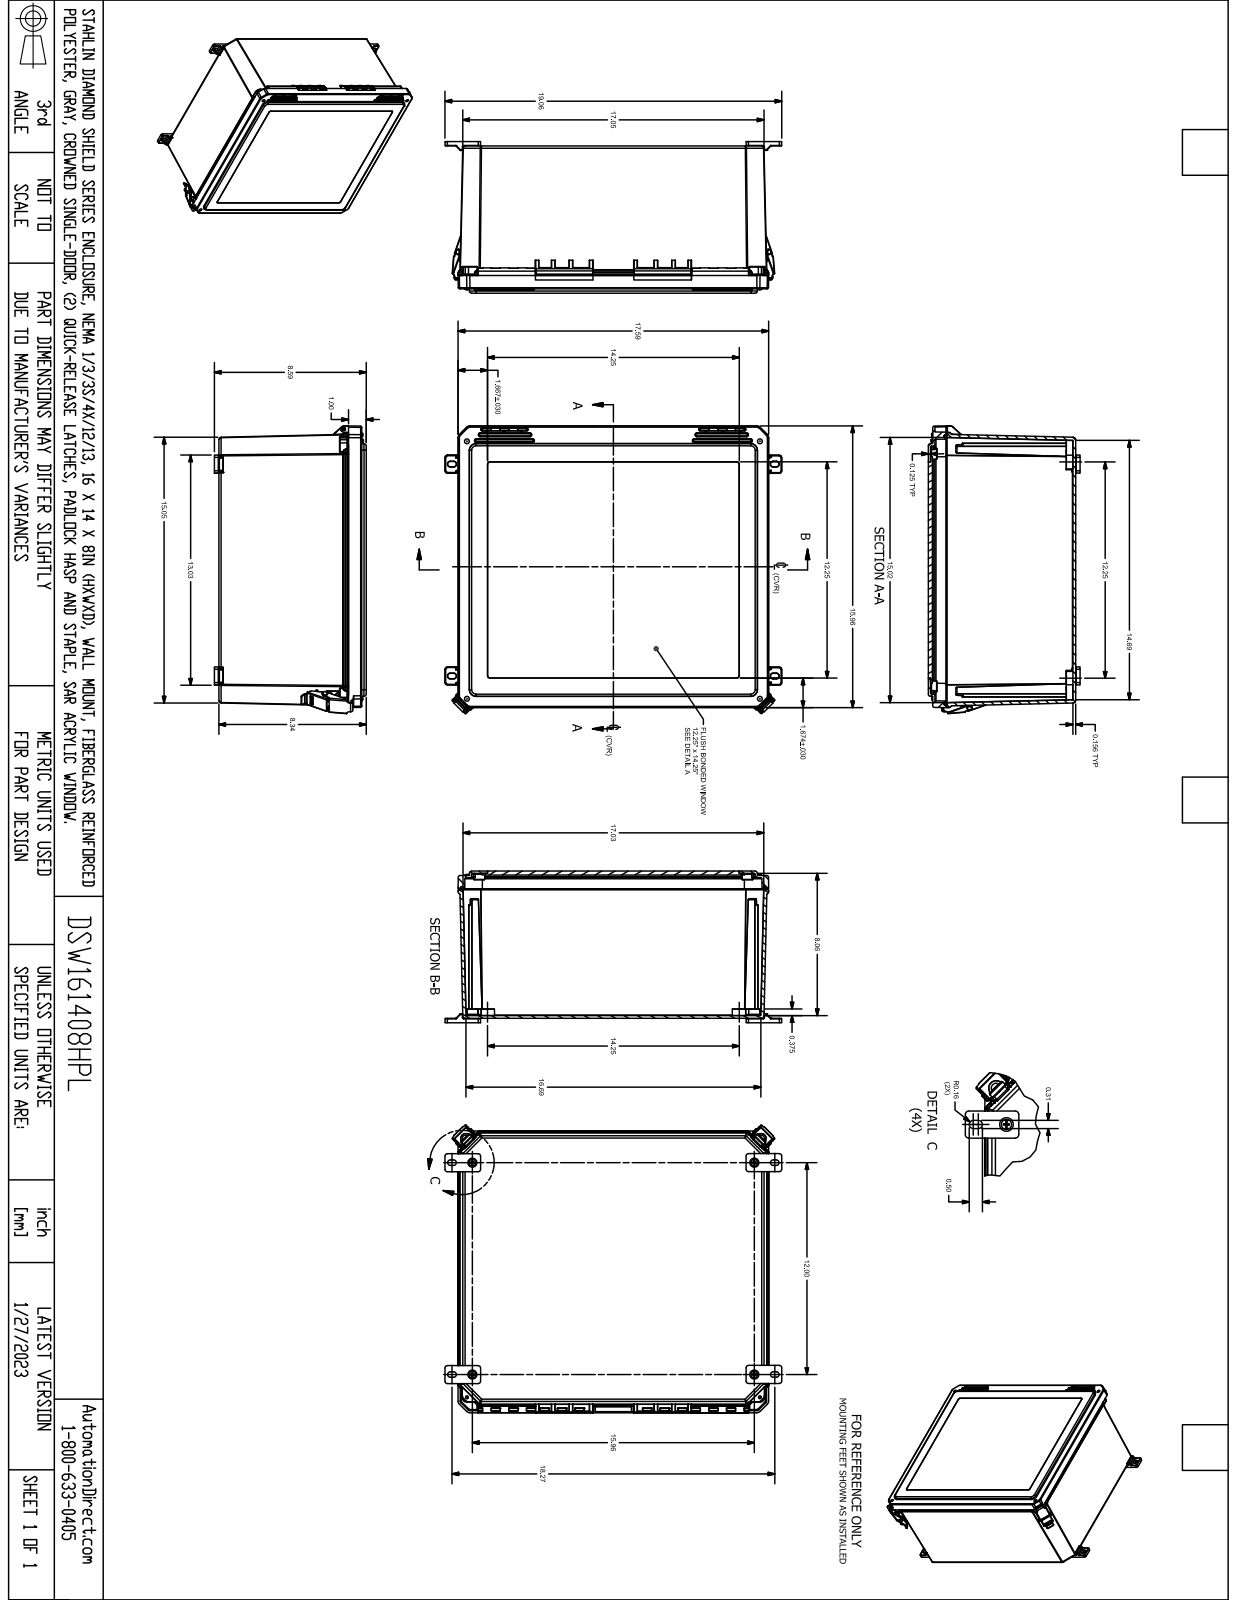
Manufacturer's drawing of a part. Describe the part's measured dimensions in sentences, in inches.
The part is named "FRW161408HPL". Its 3-D file was written by "SolidWorks 2021 (AUTOMOTIVE_DESIGN)". It is 30 solids with 2508 faces: 818 planar, 1072 cylindrical and 618 other. Overall it measures 18.253 by 16.292 by 8.84 inches. Its volume is 203.7 cubic inches and its surface area 2 297 square inches. Round holes: 10 of diameter 0.135, 8 of diameter 0.152, 8 of diameter 0.159, 4 of diameter 0.15, 4 of diameter 0.156, 4 of diameter 0.252, 4 of diameter 0.253, 3 of diameter 0.137, 2 of diameter 0.135, 2 of diameter 0.219, 2 of diameter 0.227, 2 of diameter 0.313. Round bosses or shafts: 8 of diameter 0.27, 4 of diameter 0.3, 4 of diameter 0.262, 4 of diameter 0.209, 3 of diameter 0.135, 1 of diameter 0.435, 1 of diameter 0.435. Partial cylindrical surfaces (rounded edges, fillets, slot ends): 189 of radius 0.01, 94 of radius 0.005, 70 of radius 0.02, 70 of radius 0.03, 36 of radius 0.06, 26 of radius 0.09, 26 of radius 0.125, 24 of radius 0.03. The main face-to-face distances are 0.156, 8.183, 8.339, 0.181, 0.225, 7.958, 8.114, 0.179, 0.18, 0.125. The hole center spacings are 15.461, 16.584, 16.585, 20.439, 12.155, 15.106, 19.37, 0.25.
